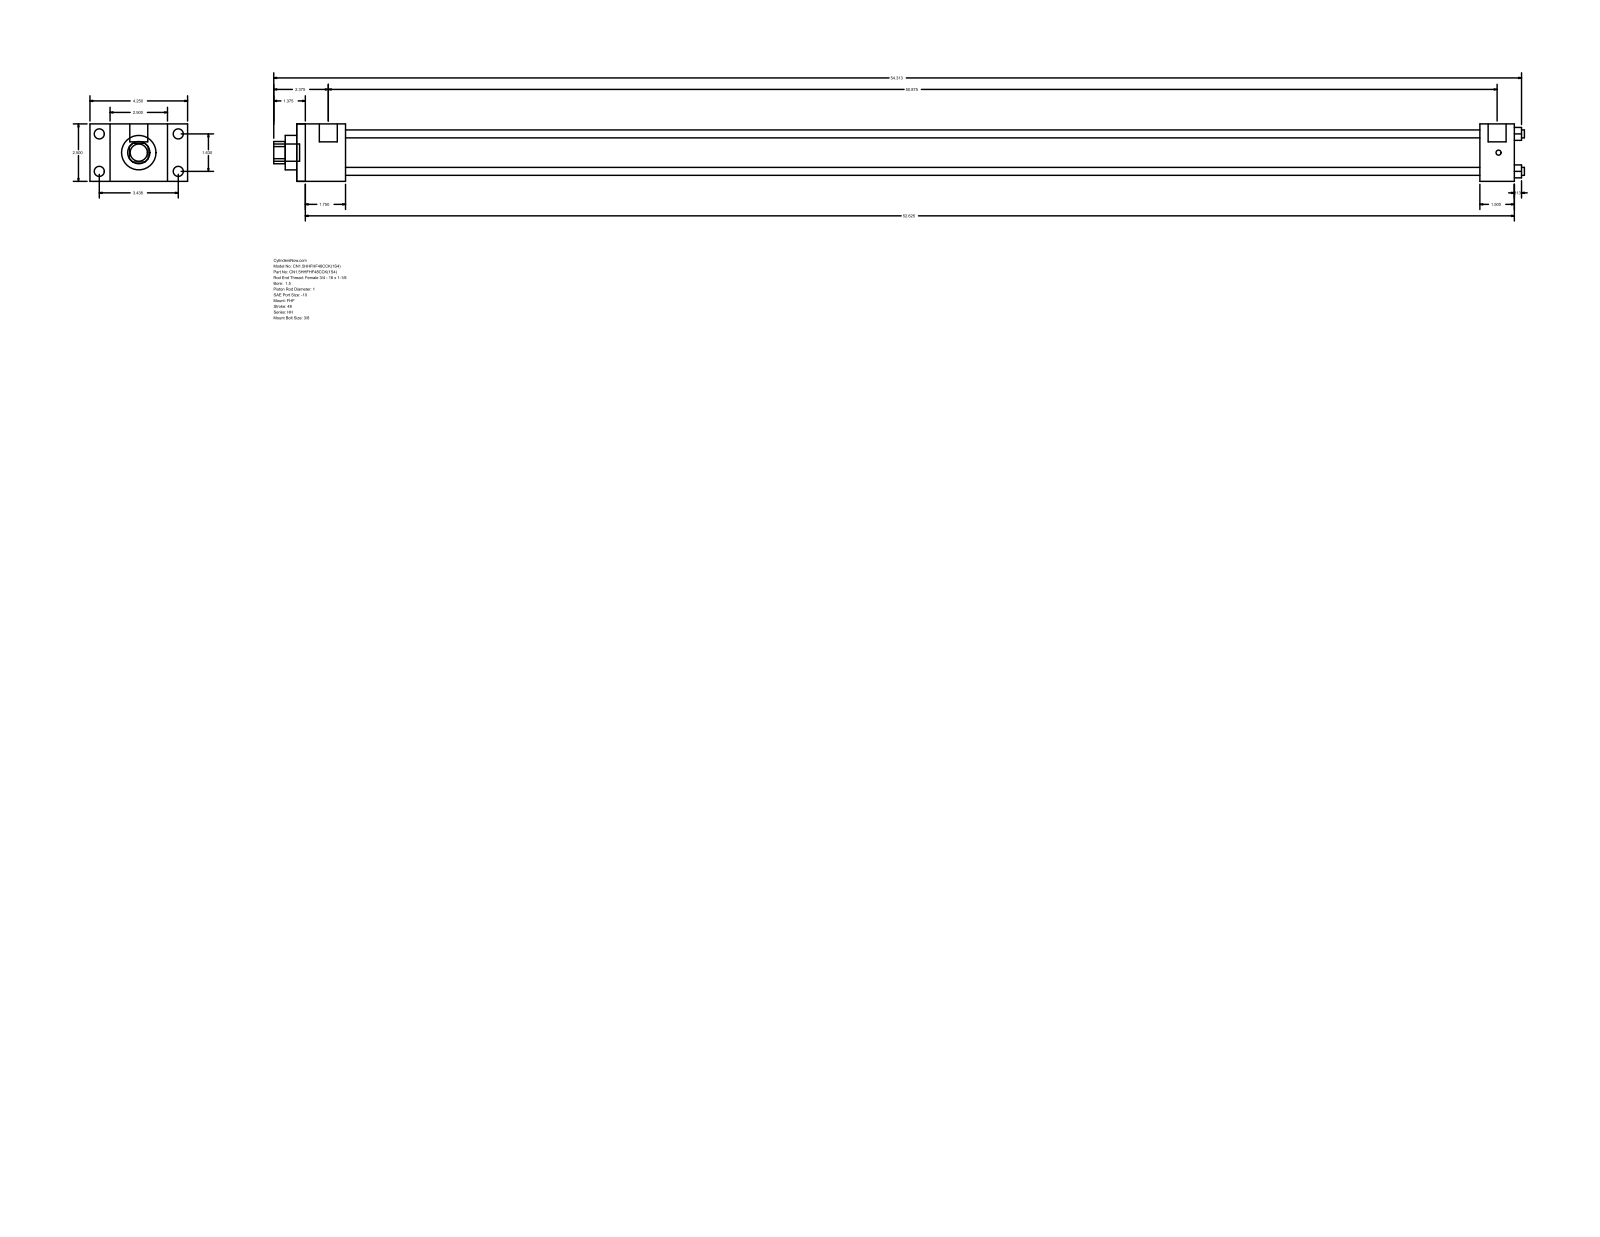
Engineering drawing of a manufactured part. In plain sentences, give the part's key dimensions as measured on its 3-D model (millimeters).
The part is named "HH_FHF__0150_1". Its 3-D file was written by "GSSL Pune (CONFIG_CONTROL_DESIGN)". It is 0 solids with 88 faces: 60 planar, 28 cylindrical and 0 other. Overall it measures 1382.71 by 107.95 by 63.5 millimeters. Round holes: 4 of diameter 8.76, 1 of diameter 25.4, 1 of diameter 38.1, 1 of diameter 44.45. Round bosses or shafts: 4 of diameter 11.13, 4 of diameter 5.56, 2 of diameter 19.84, 1 of diameter 19.05. Partial cylindrical surfaces (rounded edges, fillets, slot ends): 1 of radius 12.29. The main face-to-face distances are 63.5, 22.23, 85.73, 53.98, 107.96, 1346.2, 1292.22, 1308.1, 1254.12, 38.1. The hole center spacings are 29.27, 41.4, 58.55.
